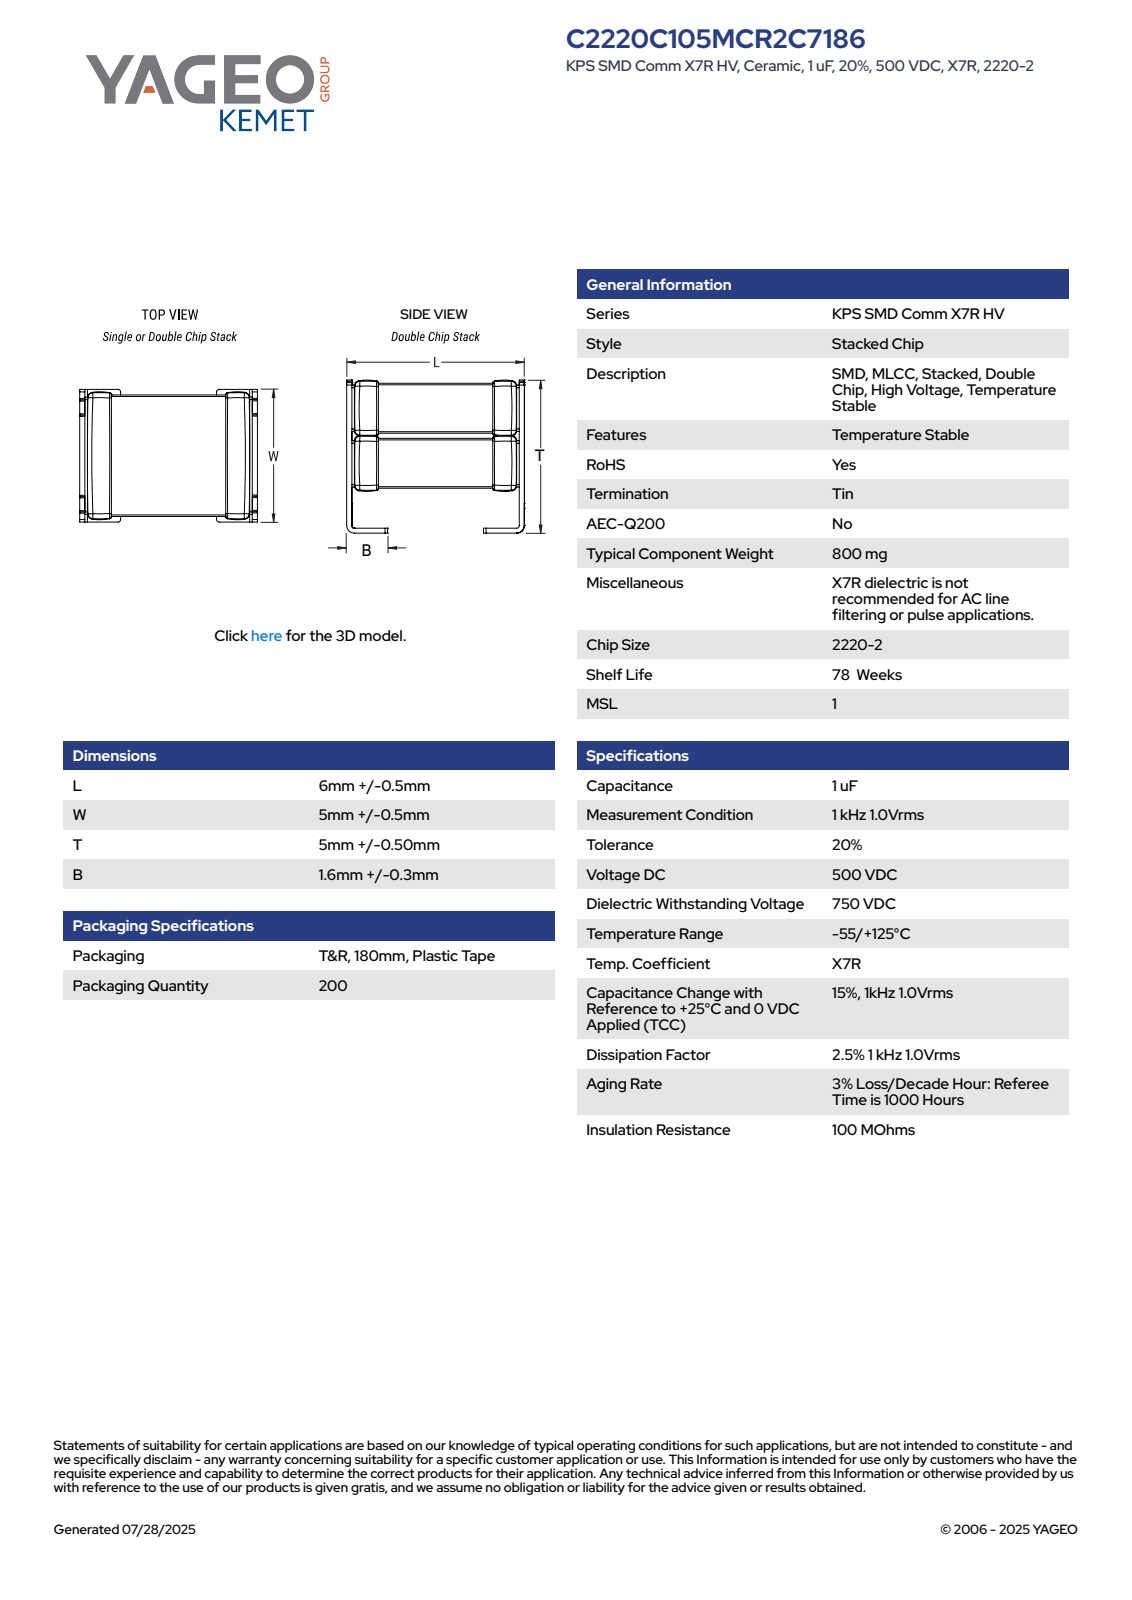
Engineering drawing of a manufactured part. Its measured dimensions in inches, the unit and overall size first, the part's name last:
Units: inches
Overall size (bounding box): 0.256 × 0.217 × 0.217
Main face-to-face distances: 0.068, 0.069, 0.069, 0.217, 0.134, 0.065, 0.066, 0.065, 0.072, 0.061
Volume: 0.007 in³ · Surface area: 0.482 in²
Bodies: 4 solids, 113 faces (109 planar, 4 cylindrical, 0 other)
Part name (STEP PRODUCT): CCSS_S2_2220-2_L6.5W5.5T5.5B1.9
STEP written by: SolidWorks 2014 (AUTOMOTIVE_DESIGN)
